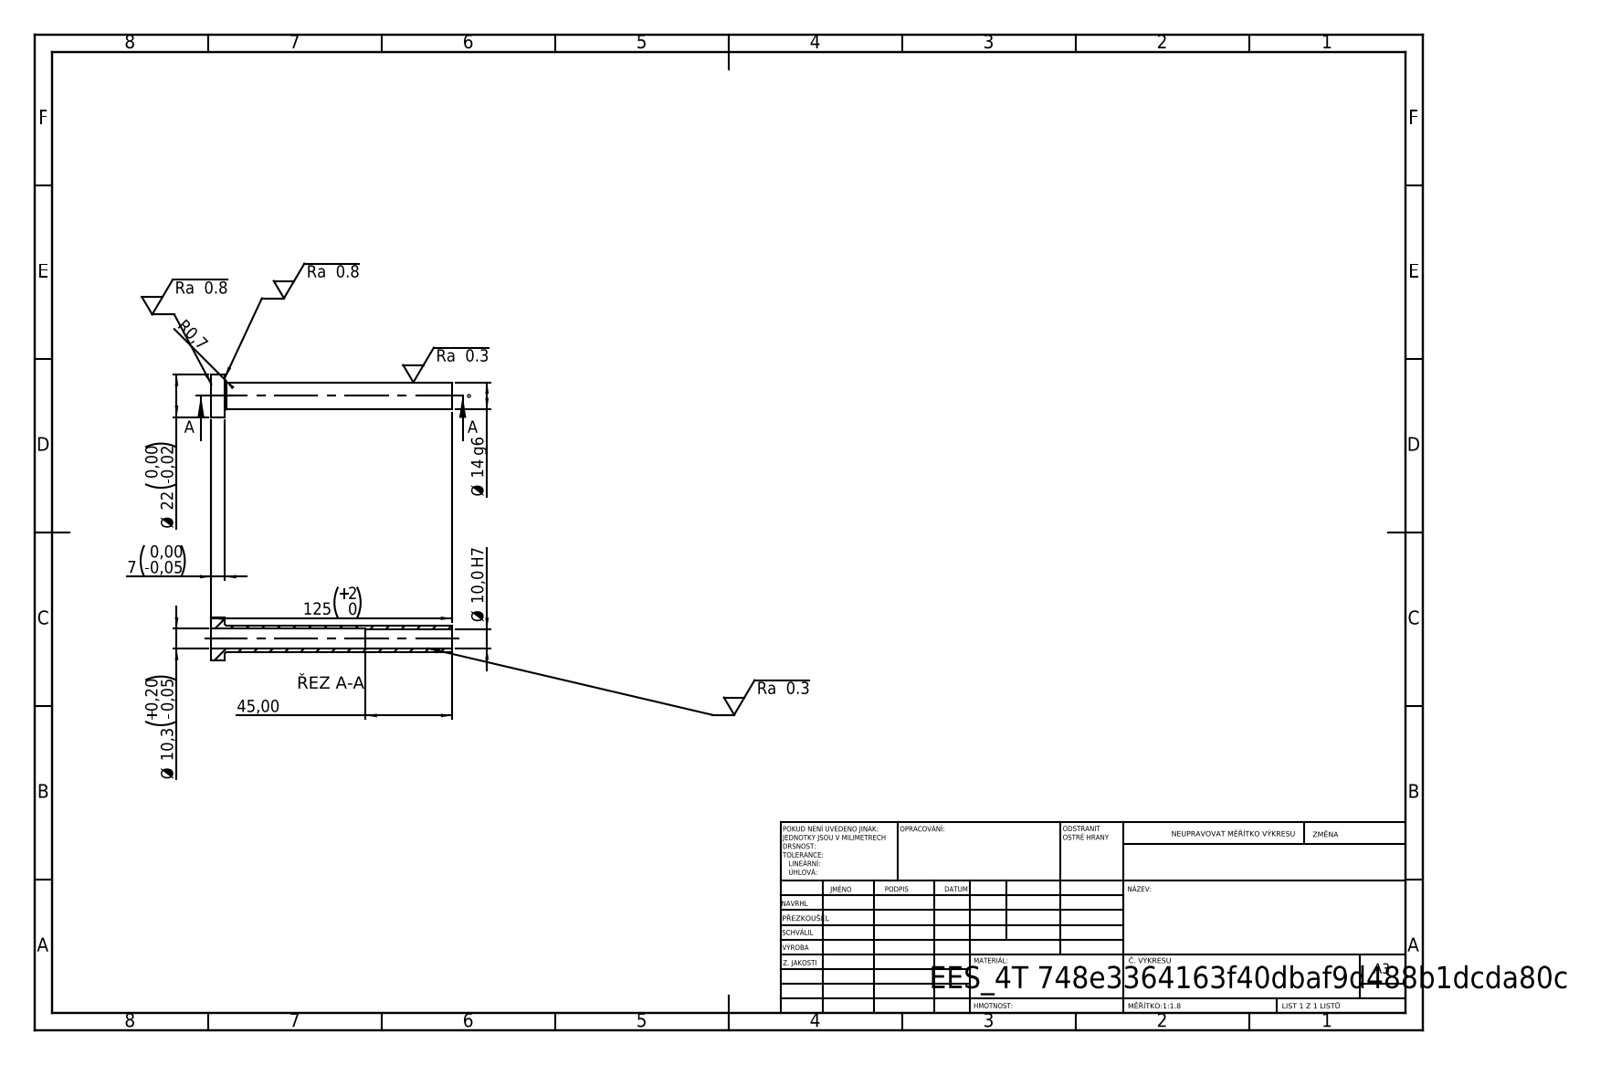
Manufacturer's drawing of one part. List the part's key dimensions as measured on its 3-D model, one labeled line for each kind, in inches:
STEP written by: SolidWorks 2019 (CONFIG_CONTROL_DESIGN)
Units: inches
Bodies: 1 solid, 14 faces (4 planar, 8 cylindrical, 2 other)
Overall size (bounding box): 4.921 × 0.866 × 0.866
Volume: 0.649 in³ · Surface area: 15.91 in²
Round holes (diameter × count): ⌀0.394 ×1, ⌀0.406 ×1
Round bosses / shafts (diameter × count): ⌀0.866 ×1, ⌀0.551 ×1
Main face-to-face distances: 0.276, 4.921, 4.646, 3.15, 2.874, 1.772
